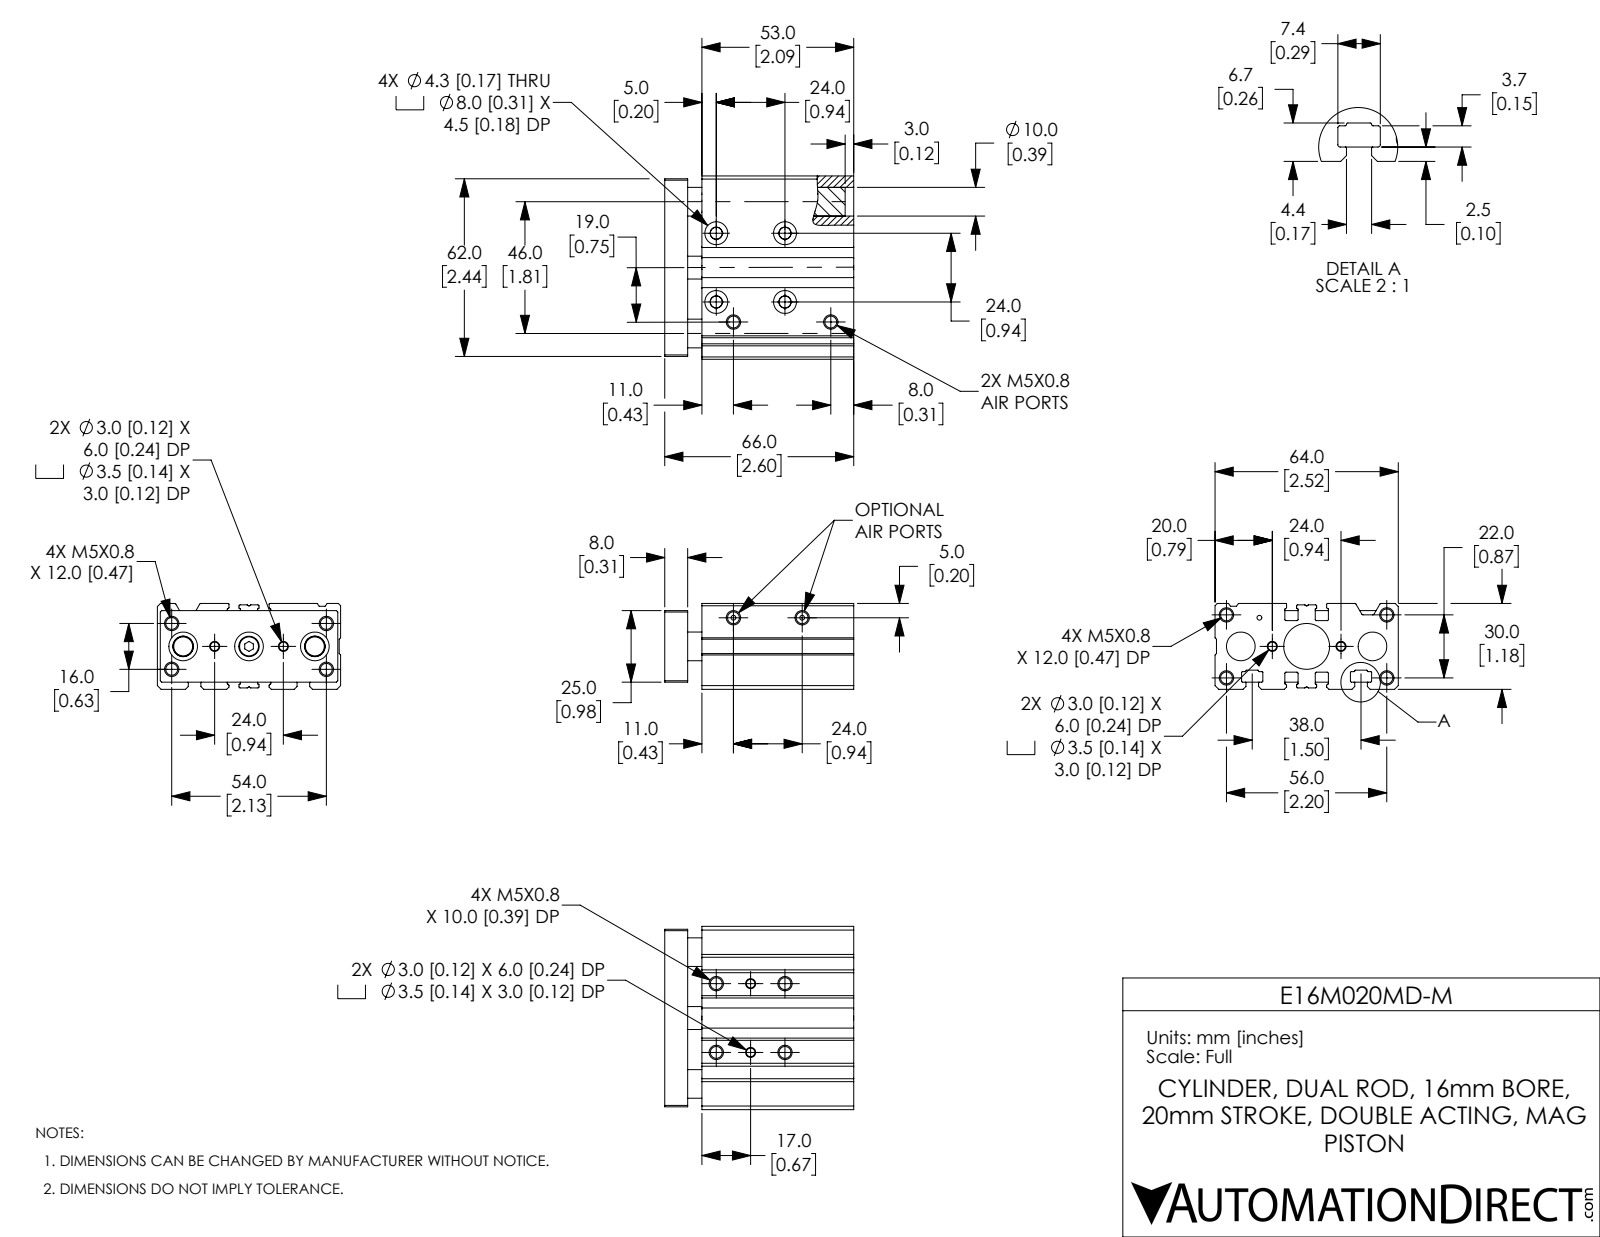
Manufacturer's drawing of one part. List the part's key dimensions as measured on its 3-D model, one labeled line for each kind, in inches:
Part name (STEP PRODUCT): E16M020MD-M_ENDPLATE; E16M020MD-M; E16M020MD-M_BODY
STEP written by: SolidWorks 2019 (CONFIG_CONTROL_DESIGN)
Units: inches
Bodies: 5 solids, 411 faces (133 planar, 192 cylindrical, 86 other)
Overall size (bounding box): 2.598 × 2.52 × 1.181
Volume: 5.784 in³ · Surface area: 60.3 in²
Round holes (diameter × count): ⌀0.163 ×16, ⌀0.118 ×4, ⌀0.138 ×4, ⌀0.169 ×4, ⌀0.315 ×4, ⌀0.066 ×3, ⌀0.197 ×3, ⌀0.394 ×3, ⌀0.28 ×2, ⌀0.394 ×1, ⌀0.63 ×1, ⌀0.63 ×1
Round bosses / shafts (diameter × count): ⌀0.315 ×1, ⌀0.28 ×1
Partial cylindrical surfaces — rounded edges, fillets, slot ends (radius × count): R0.008 ×22, R0.016 ×20, R0.01 ×8, R0.012 ×6, R0.02 ×4
Main face-to-face distances: 1.181, 0.02, 1.083, 2.283, 0.197, 0.512, 0.138, 0.315, 2.598, 2.087
Hole centre spacings: 0.945, 0.472, 0.124, 0.352, 0.476, 0.669, 0.749, 0.765
